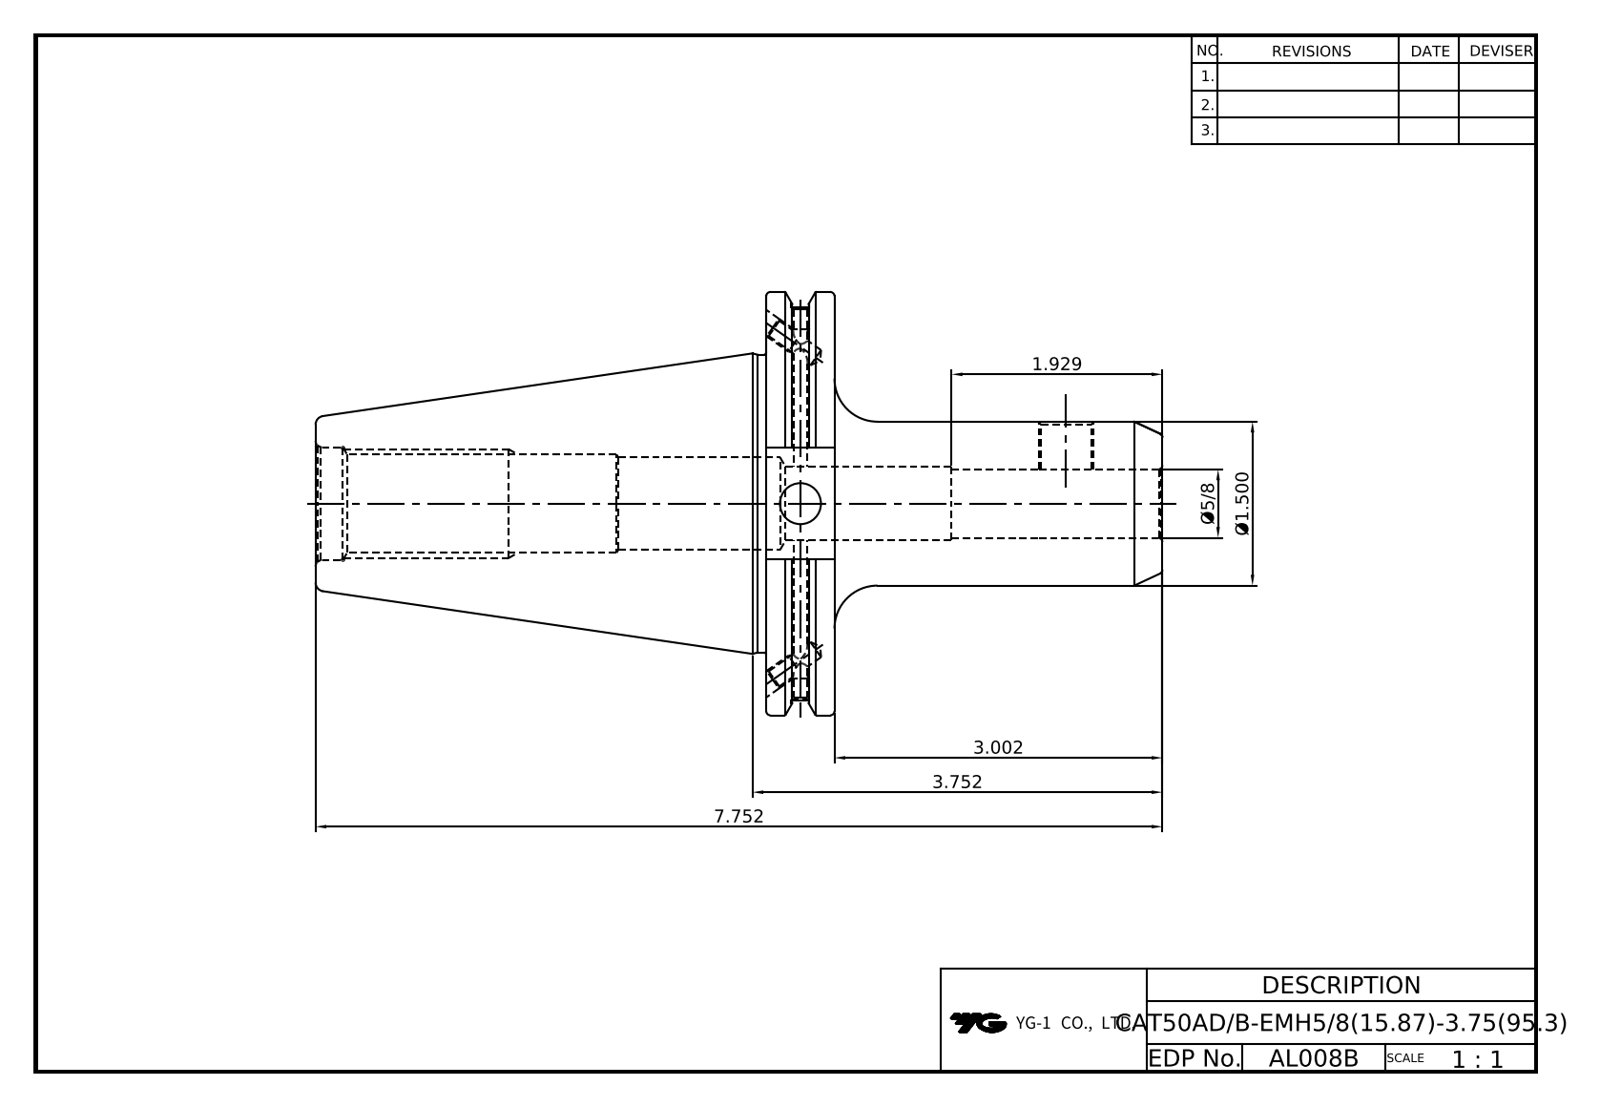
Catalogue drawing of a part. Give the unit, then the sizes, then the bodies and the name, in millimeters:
Units: millimetres
Overall size (bounding box): 196.9 × 98.42 × 94.69
Round holes (diameter × count): ⌀4.13 ×2, ⌀4.2 ×2, ⌀5 ×2, ⌀9.53 ×1, ⌀11.33 ×1, ⌀17 ×1, ⌀18 ×1, ⌀21.97 ×1, ⌀26.2 ×1
Round bosses / shafts (diameter × count): ⌀98.42 ×1, ⌀91.29 ×1, ⌀69.25 ×1, ⌀38.1 ×1
Main face-to-face distances: 15.88, 104.77, 120.65, 196.9, 92.13, 76.25, 73.03, 25.9, 110.82, 6.05
Volume: 388 401 mm³ · Surface area: 57 260 mm²
Bodies: 1 solid, 81 faces (35 planar, 22 cylindrical, 24 other)
Part name (STEP PRODUCT): LO-CAT50ADB-EMH15.875-95.3
STEP written by: Autodesk Inventor 2025 (AUTOMOTIVE_DESIGN)
